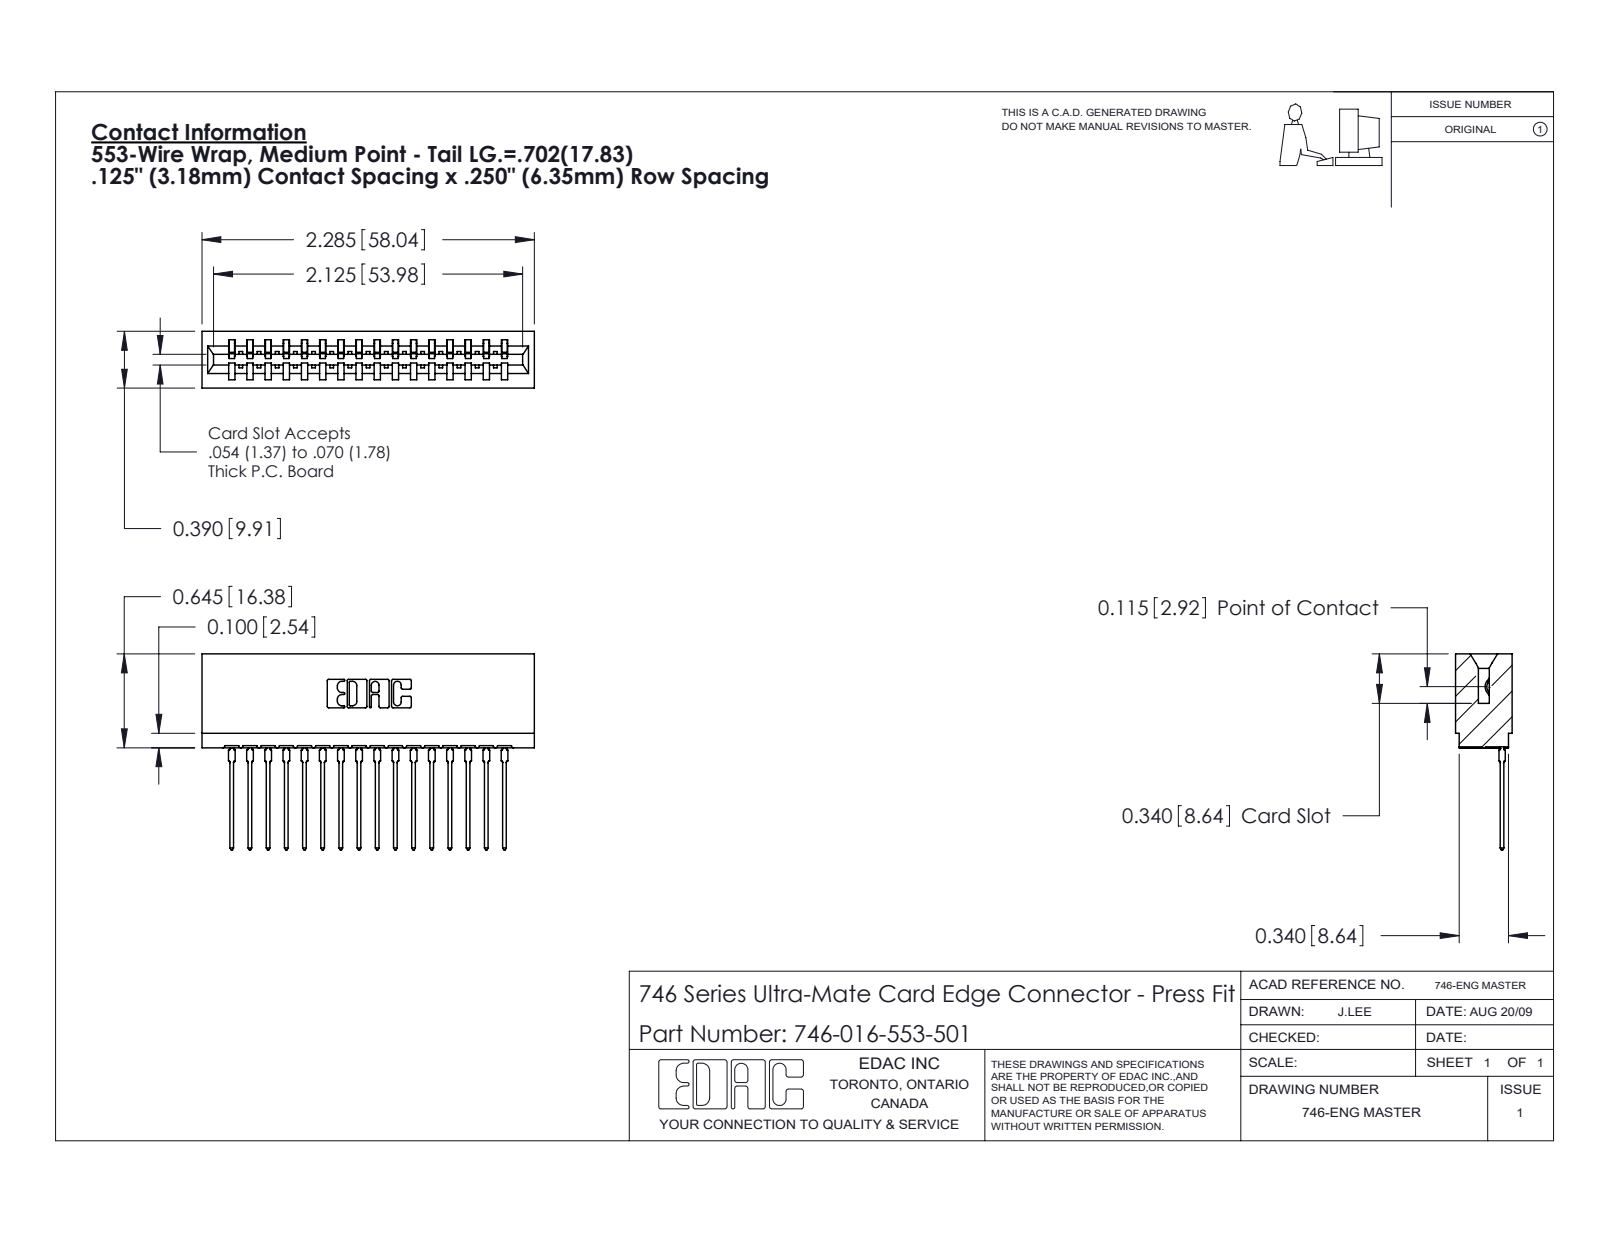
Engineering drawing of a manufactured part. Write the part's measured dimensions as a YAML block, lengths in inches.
part_name: "746-016-553-501; 746-292-001_553; 746 Part_.340 Slot Depth - 01"
step_written_by: "SolidWorks 2020 (CONFIG_CONTROL_DESIGN)"
units: inches
bodies: {solids: 17, faces: 1825, planar: 1063, cylindrical: 346, other: 416}
overall_size: [2.285, 1.346, 0.39]
volume: 0.411
surface_area: 13.93
partial_cylinders:
  - {radius: 0.021, count: 32}
  - {radius: 0.01, count: 22}
  - {radius: 0.015, count: 17}
  - {radius: 0.007, count: 6}
  - {radius: 0.031, count: 6}
  - {radius: 0.005, count: 4}
  - {radius: 0.011, count: 4}
  - {radius: 0.026, count: 3}
face_to_face_distances: [0.25, 0.057, 0.333, 0.5, 0.39, 0.125, 0.025, 0.307, 0.125, 0.292]
